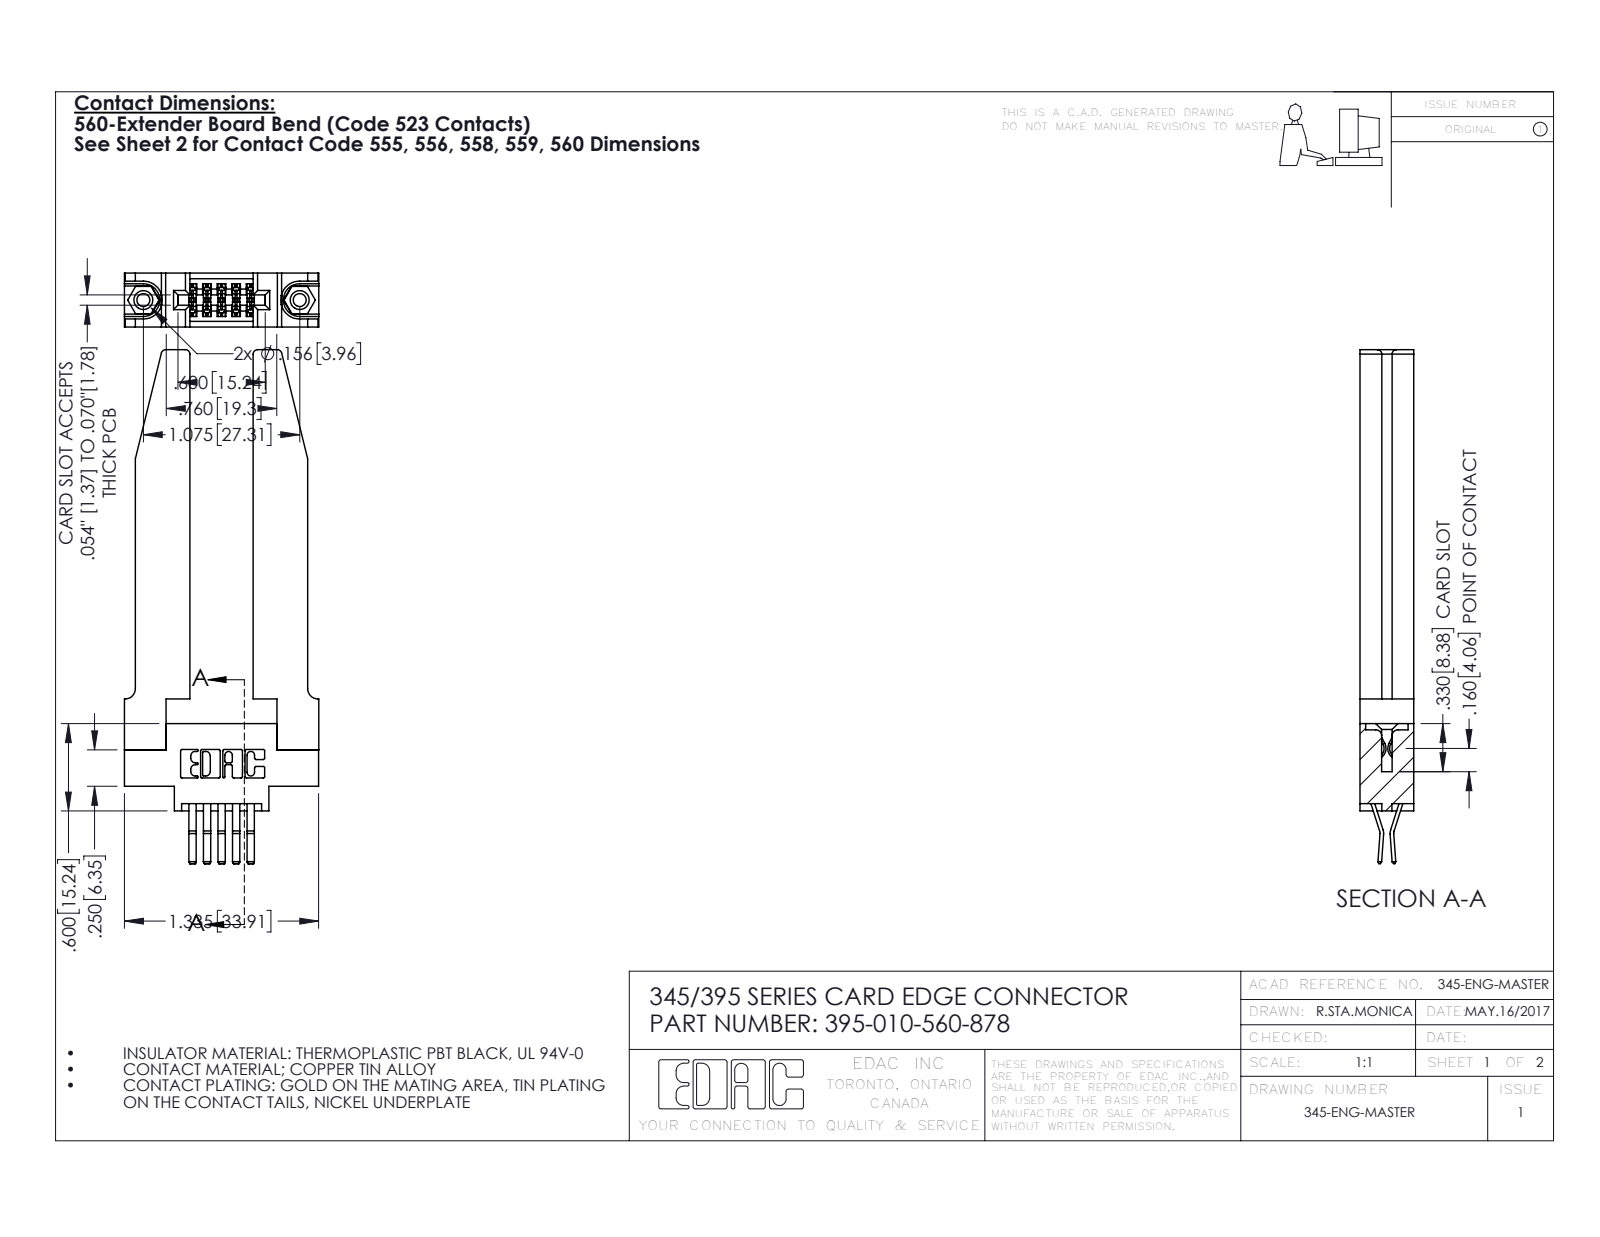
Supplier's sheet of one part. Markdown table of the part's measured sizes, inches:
| quantity | value |
| --- | --- |
| part name | 345 Part_0.170 Offset - 0.156 Dia-TH; 345-292-001_560 Tail; 345-250-001_345-250-001-102; 395-010-560-878 (+1 more) |
| STEP written by | SolidWorks 2016 (CONFIG_CONTROL_DESIGN) |
| units | inches |
| bodies | 15 solids, 884 faces (556 planar, 276 cylindrical, 52 other) |
| overall size | 3.532 × 1.336 × 0.37 |
| volume | 0.651 in³ |
| surface area | 16.63 in² |
| round holes (diameter × count) | 0.089 × 2, 0.125 × 2, 0.156 × 2, 0.064 × 1 |
| round bosses / shafts (diameter × count) | 0.155 × 2 |
| partial cylindrical surfaces (radius × count) | 0.01 × 22, 0.006 × 15, 0.03 × 8, 0.007 × 6, 0.031 × 6, 0.026 × 3, 0.01 × 2, 0.014 × 2 |
| main face-to-face distances | 0.37, 0.15, 0.22, 0.435, 0.072, 0.148, 0.298, 0.077, 0.095, 0.025 |
| hole center spacings | 0.27, 0.847, 1.075 |
